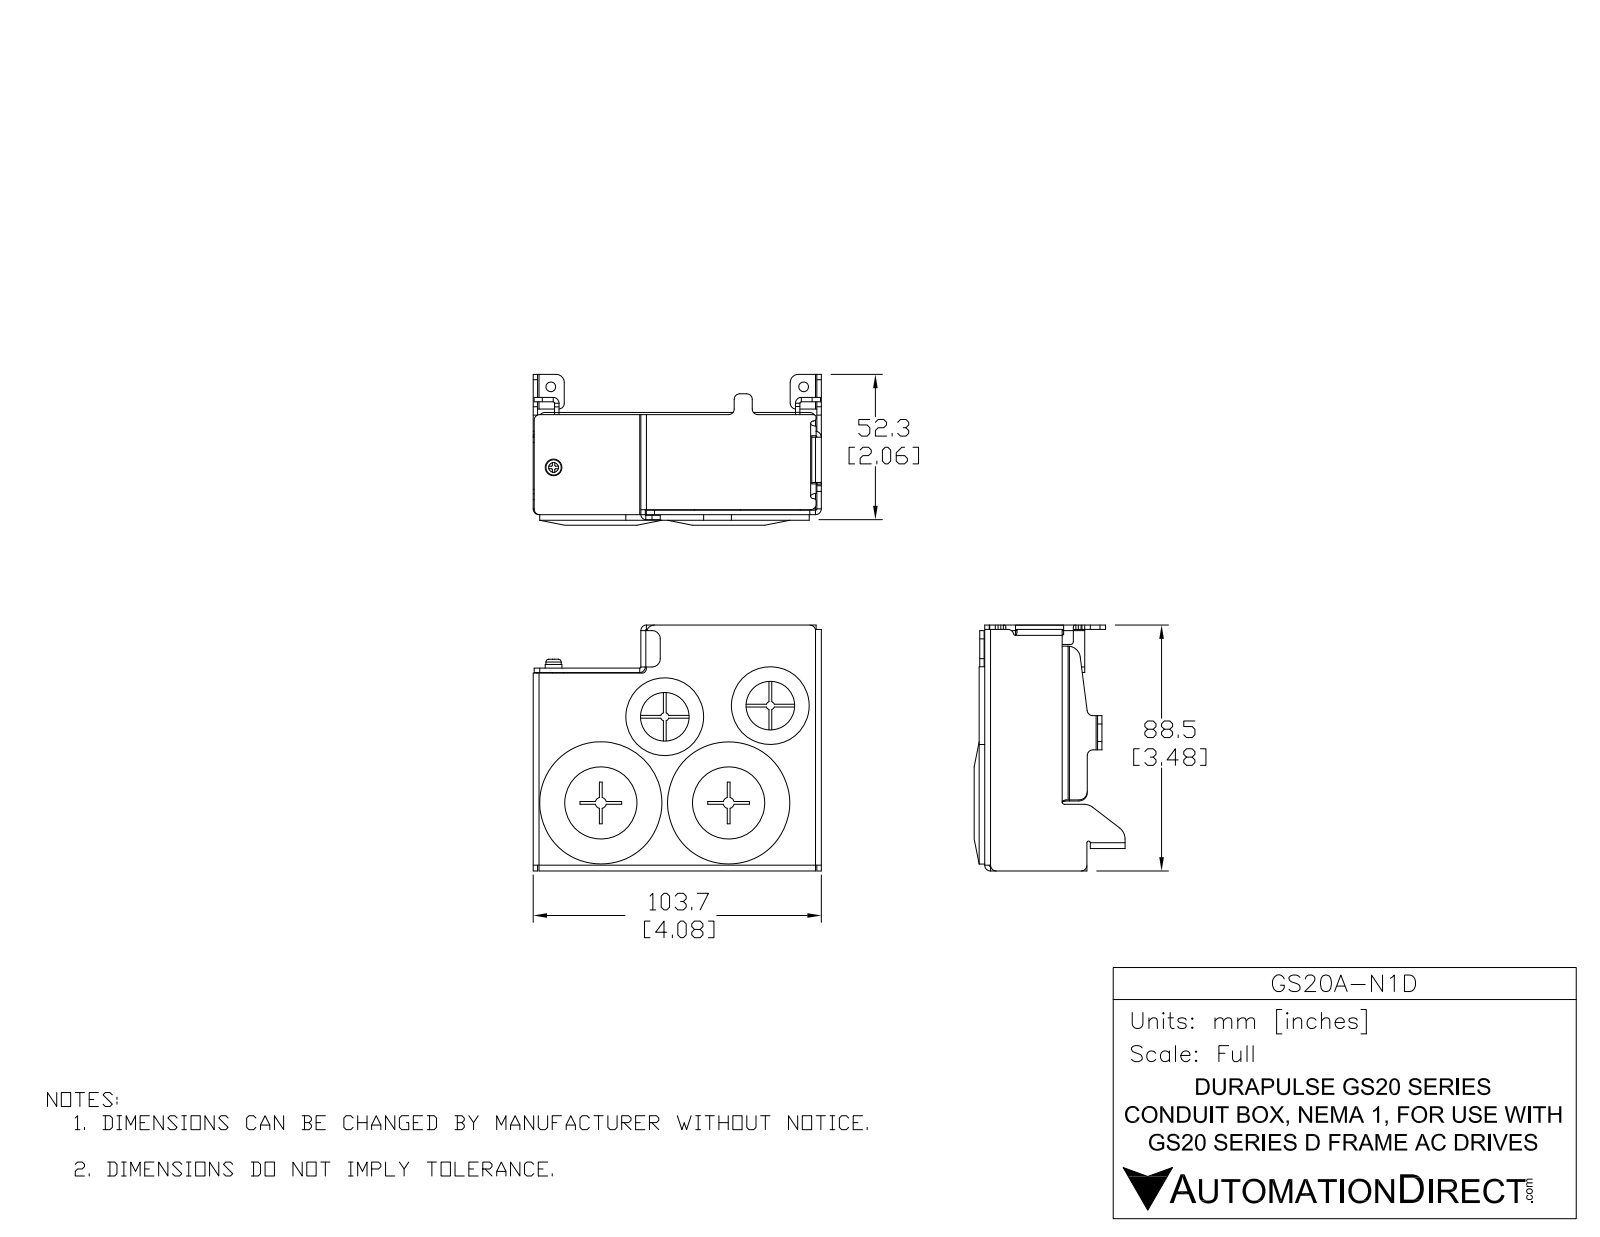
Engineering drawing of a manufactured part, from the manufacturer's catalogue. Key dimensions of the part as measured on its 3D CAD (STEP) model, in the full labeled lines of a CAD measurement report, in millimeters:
Part name (STEP PRODUCT): GS20A-NID
STEP written by: SolidWorks 2017 (AUTOMOTIVE_DESIGN)
Units: millimetres
Bodies: 8 solids, 397 faces (199 planar, 167 cylindrical, 31 other)
Overall size (bounding box): 103.7 × 88.5 × 54.3
Volume: 48 100 mm³ · Surface area: 58 760 mm²
Round holes (diameter × count): ⌀3.5 ×2, ⌀17.5 ×2, ⌀22.5 ×2, ⌀26.5 ×2, ⌀34.5 ×2, ⌀2.5 ×1, ⌀3 ×1, ⌀4 ×1
Round bosses / shafts (diameter × count): ⌀44 ×2, ⌀33.5 ×2, ⌀28 ×2, ⌀21.5 ×2, ⌀6 ×1, ⌀5.6 ×1, ⌀5.5 ×1, ⌀4.9 ×1
Partial cylindrical surfaces — rounded edges, fillets, slot ends (radius × count): R2.1 ×25, R2 ×14, R0.5 ×13, R3 ×11, R1 ×5, R0.3 ×4, R0.4 ×3, R0.6 ×3
Main face-to-face distances: 1.6, 86.9, 102.1, 15.5, 71.4, 85.3, 88.5, 100.5, 103.7, 17.1
Hole centre spacings: 38.6, 29, 38.1, 38.2, 46, 70.3, 91, 94.6
